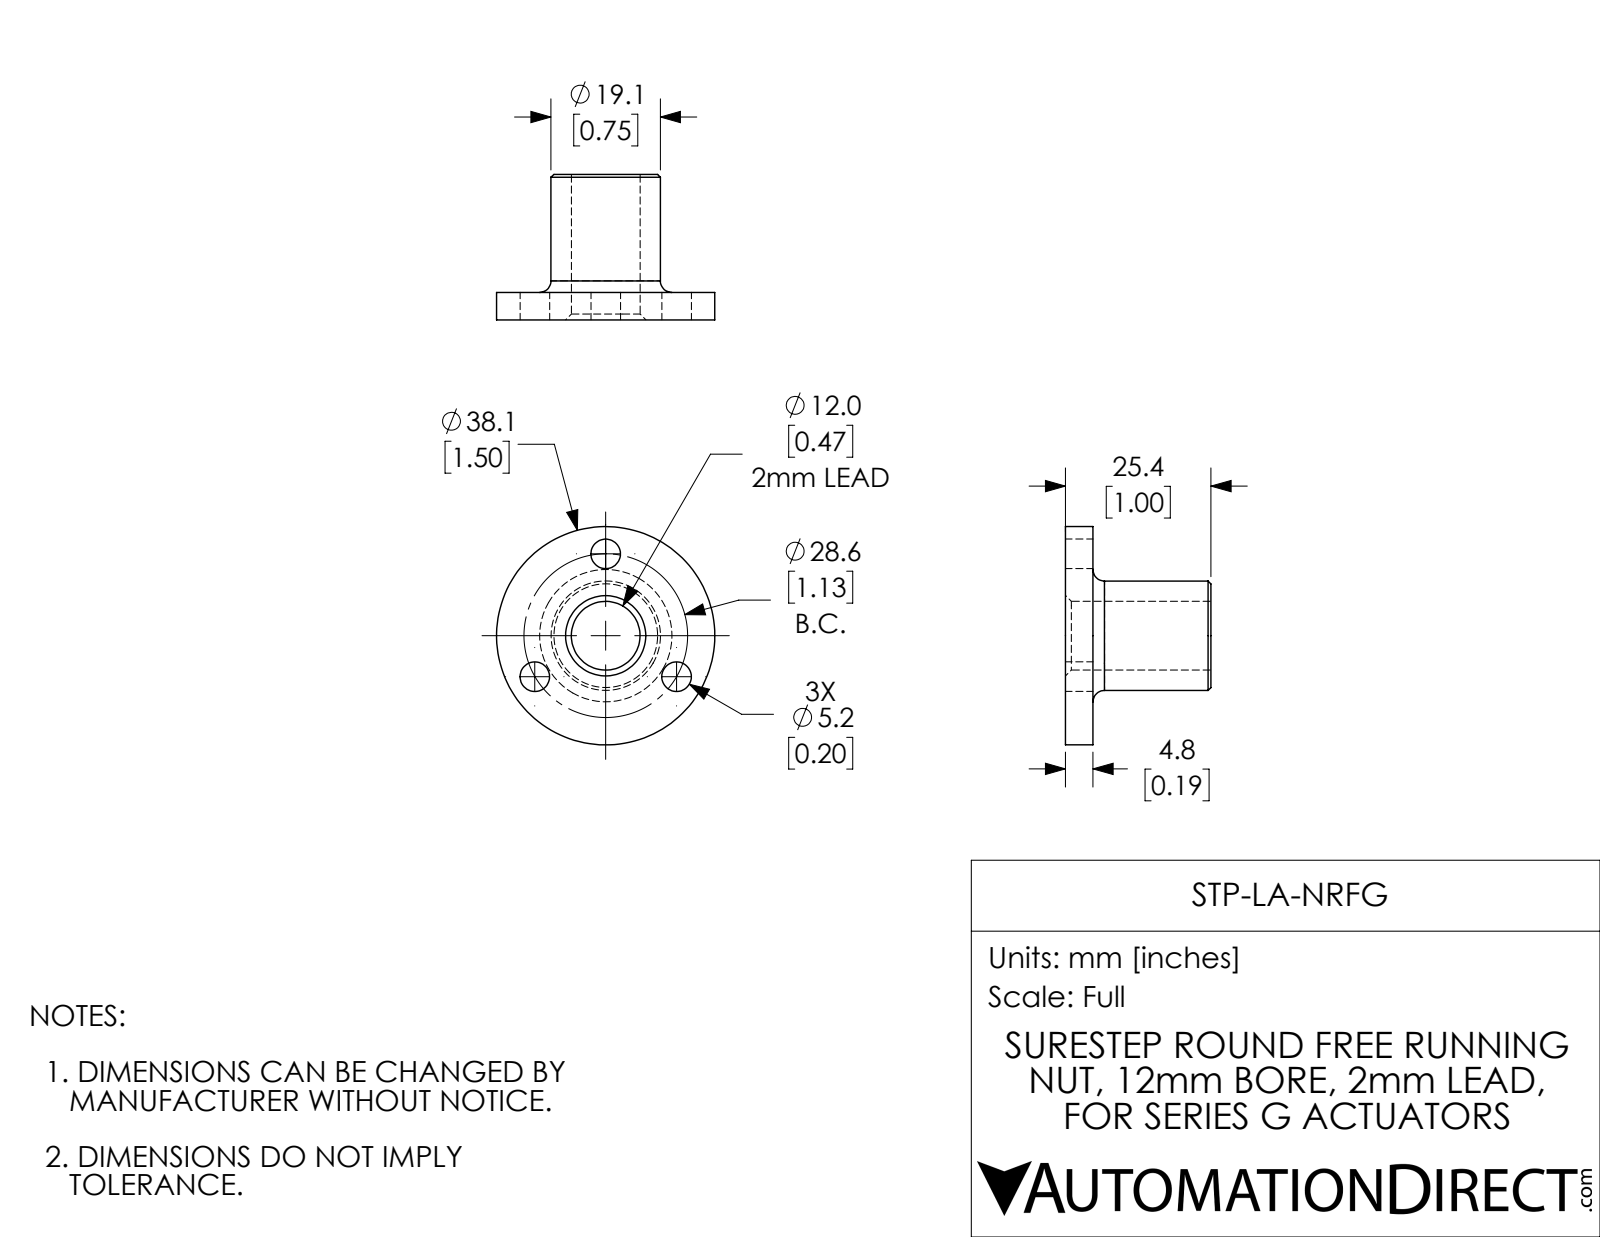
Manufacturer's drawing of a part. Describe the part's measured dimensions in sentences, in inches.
The part is named "STP-LA-NRFG". Its 3-D file was written by "SolidWorks 2017 (AUTOMOTIVE_DESIGN)". It is 1 solid with 21 faces: 3 planar, 12 cylindrical and 6 other. Overall it measures 1.5 by 1.5 by 1 inches. Its volume is 0.502 cubic inches and its surface area 7.505 square inches. Round holes: 3 of diameter 0.203, 1 of diameter 0.472. Round bosses or shafts: 1 of diameter 1.5, 1 of diameter 0.752. The main face-to-face distances are 0.189, 0.811, 1. The hole center spacings are 0.563, 0.974, 0.562, 0.974.
